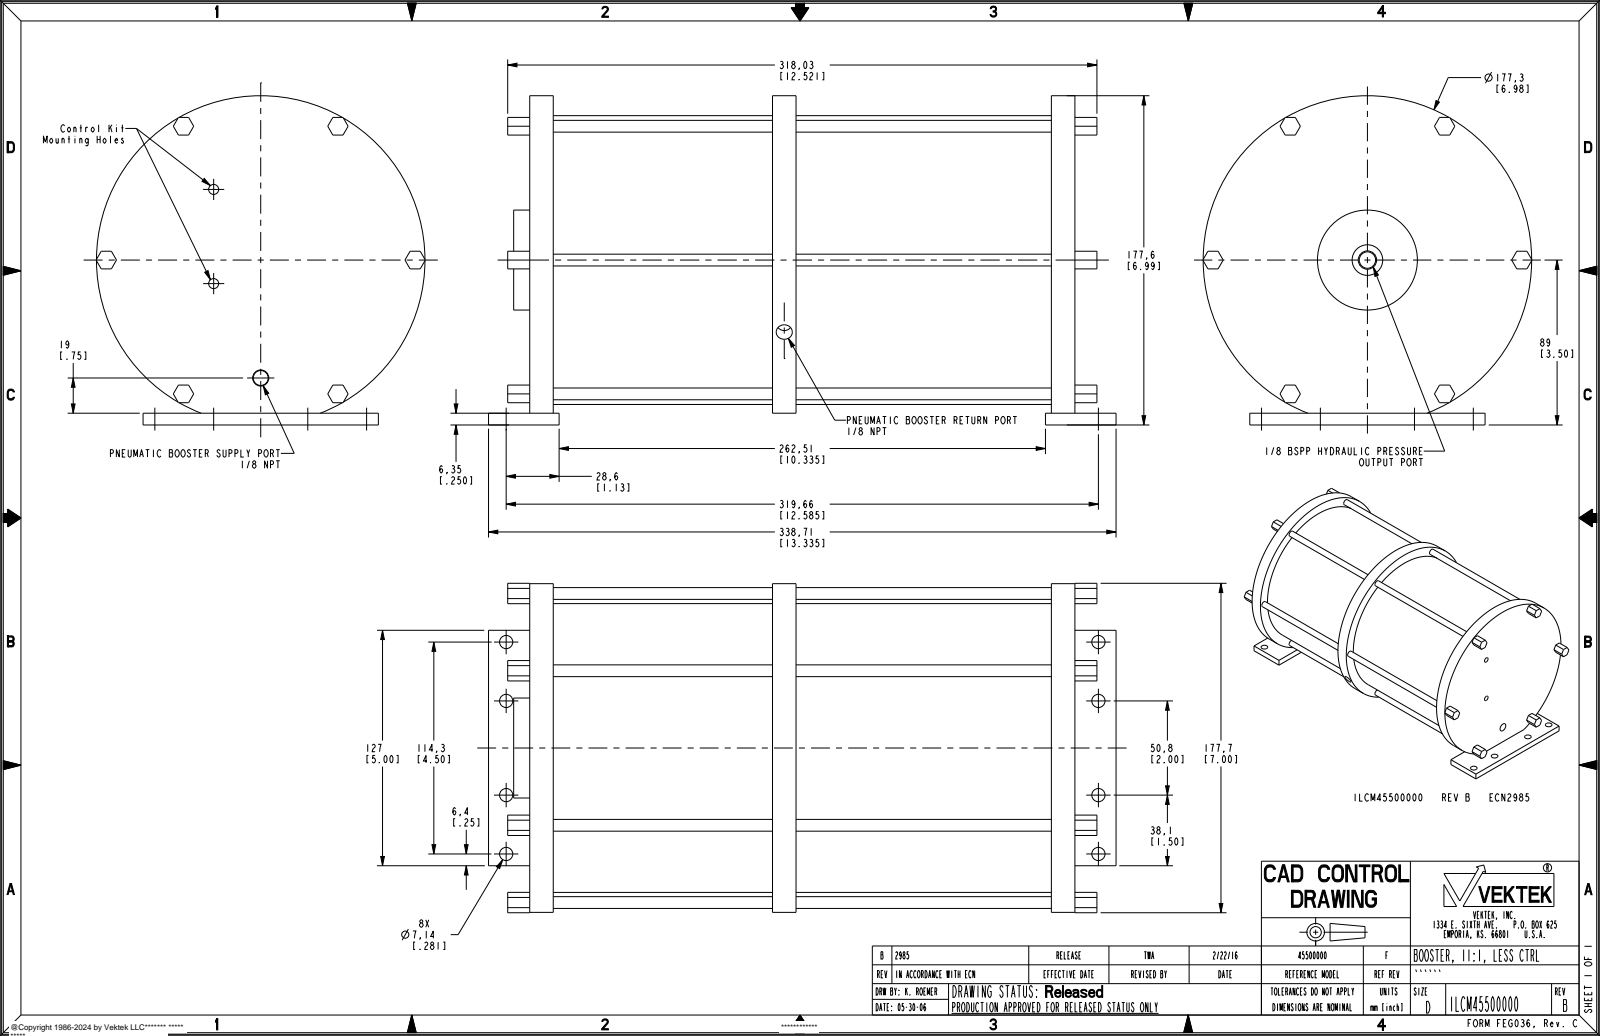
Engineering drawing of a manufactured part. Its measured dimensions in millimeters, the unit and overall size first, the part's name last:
Units: millimetres
Overall size (bounding box): 338.71 × 177.7 × 177.6
Round holes (diameter × count): ⌀7.14 ×12, ⌀6.35 ×6, ⌀5.11 ×4, ⌀5.41 ×2, ⌀8.84 ×1, ⌀16.51 ×1
Round bosses / shafts (diameter × count): ⌀6.35 ×6, ⌀177.29 ×1, ⌀155.78 ×1, ⌀53.92 ×1, ⌀9.73 ×1
Main face-to-face distances: 294.26, 12.7, 281.56, 131.04, 150.52, 6.35, 143.74, 118.34, 268.86, 163.22
Hole centre spacings: 50.8, 19.05, 31.75, 37.03, 54.25, 82.55, 84.72, 300.61
Volume: 5 946 000 mm³ · Surface area: 278 463 mm²
Bodies: 1 solid, 243 faces (128 planar, 87 cylindrical, 28 other)
Part name (STEP PRODUCT): ILCM45500000
STEP written by: PRO/ENGINEER BY PARAMETRIC TECHNOLOGY CORPORATION, 2013320 (CONFIG_CONTROL_DESIGN)
